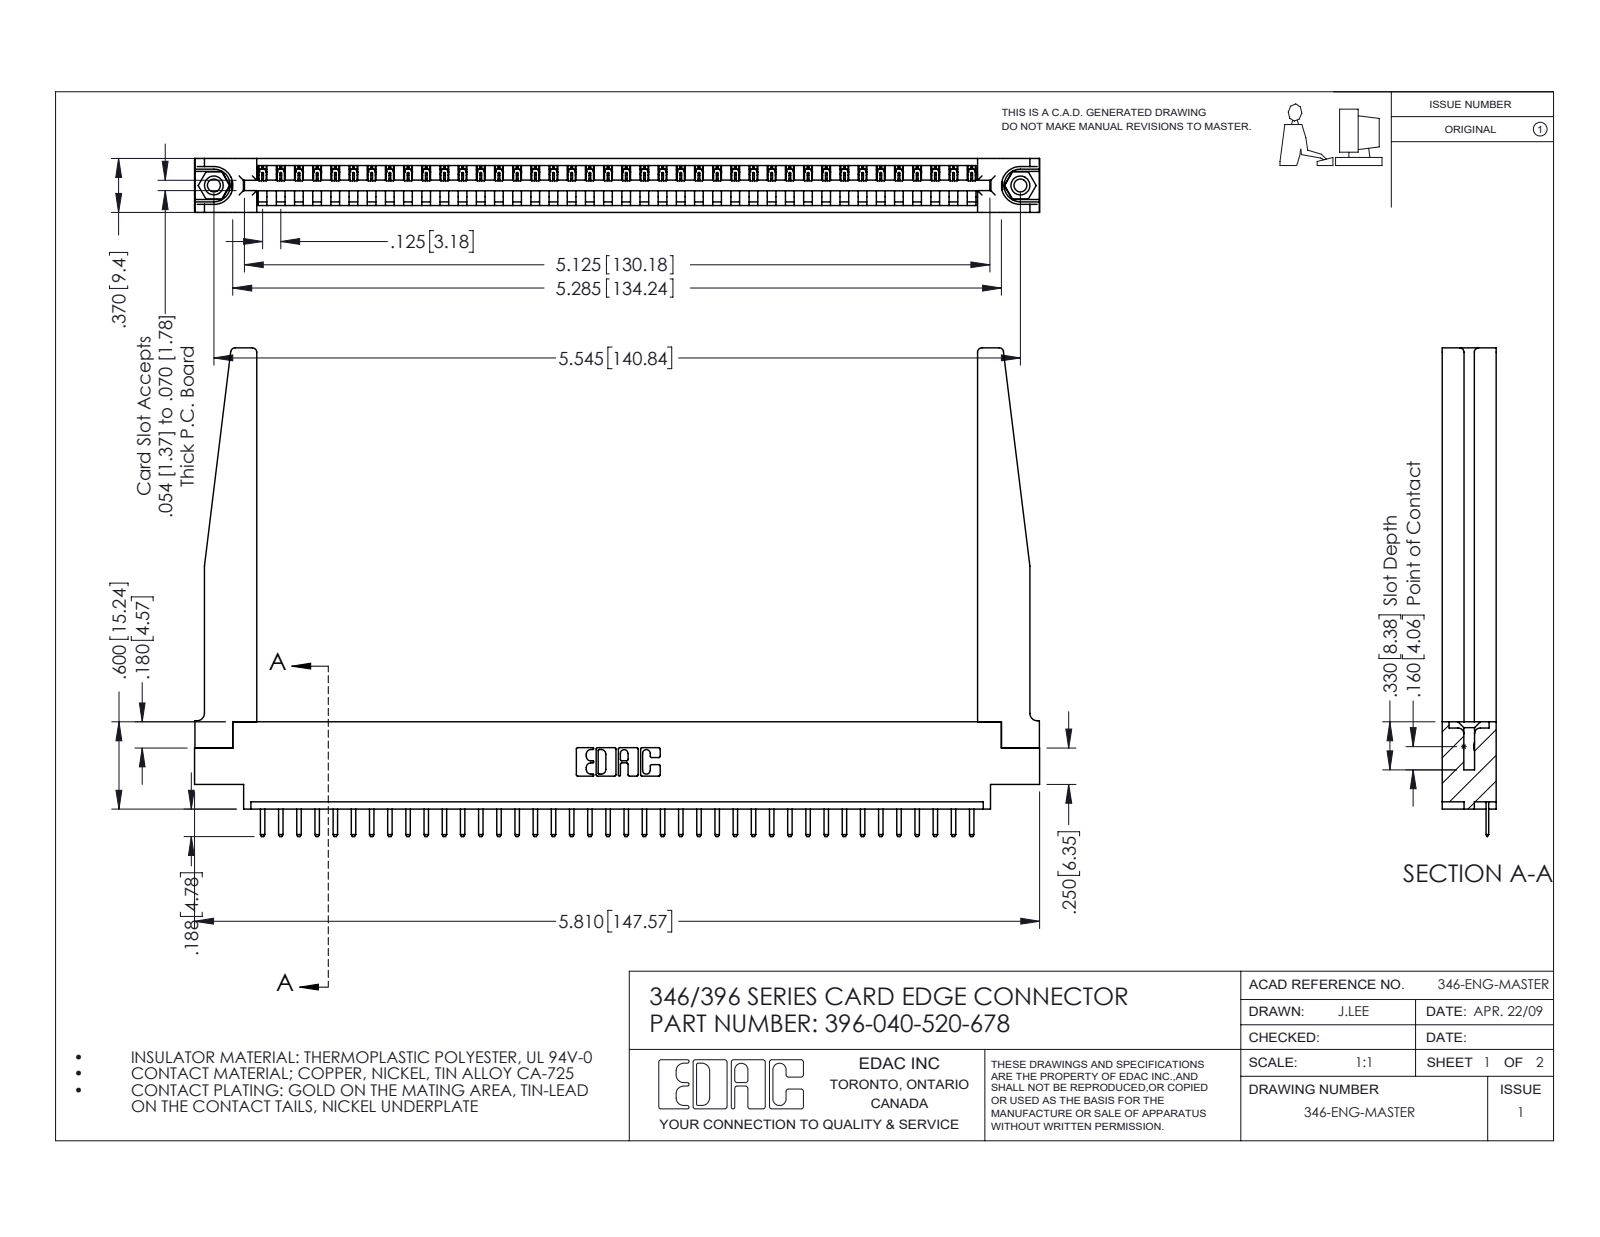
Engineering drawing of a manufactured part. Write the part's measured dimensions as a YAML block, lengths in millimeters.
part_name: "396-040-520-678; 346-220-078_345-220-078; 346 Part_0.170 Offset - 0.156 Dia-TH; 345-250-001_345-250-001-102 (+1 more)"
step_written_by: "SolidWorks 2016 (CONFIG_CONTROL_DESIGN)"
units: millimeters
bodies: {solids: 45, faces: 2840, planar: 1902, cylindrical: 886, other: 52}
overall_size: [147.6, 85.3, 9.4]
volume: 20750
surface_area: 23590
round_holes:
  - {diameter: 2.3, count: 2}
  - {diameter: 3.2, count: 2}
  - {diameter: 4, count: 2}
  - {diameter: 1.6, count: 1}
round_bosses_or_shafts:
  - {diameter: 3.9, count: 2}
partial_cylinders:
  - {radius: 0.3, count: 82}
  - {radius: 0.2, count: 80}
  - {radius: 0.3, count: 22}
  - {radius: 0.8, count: 8}
  - {radius: 0.2, count: 6}
  - {radius: 0.8, count: 6}
  - {radius: 0.7, count: 3}
  - {radius: 0.8, count: 2}
face_to_face_distances: [9.4, 1.2, 8.2, 3.8, 1.8, 3.8, 6.4, 5.6, 2.5, 4.4]
hole_center_spacings: [6.2, 135.5, 140.8]
